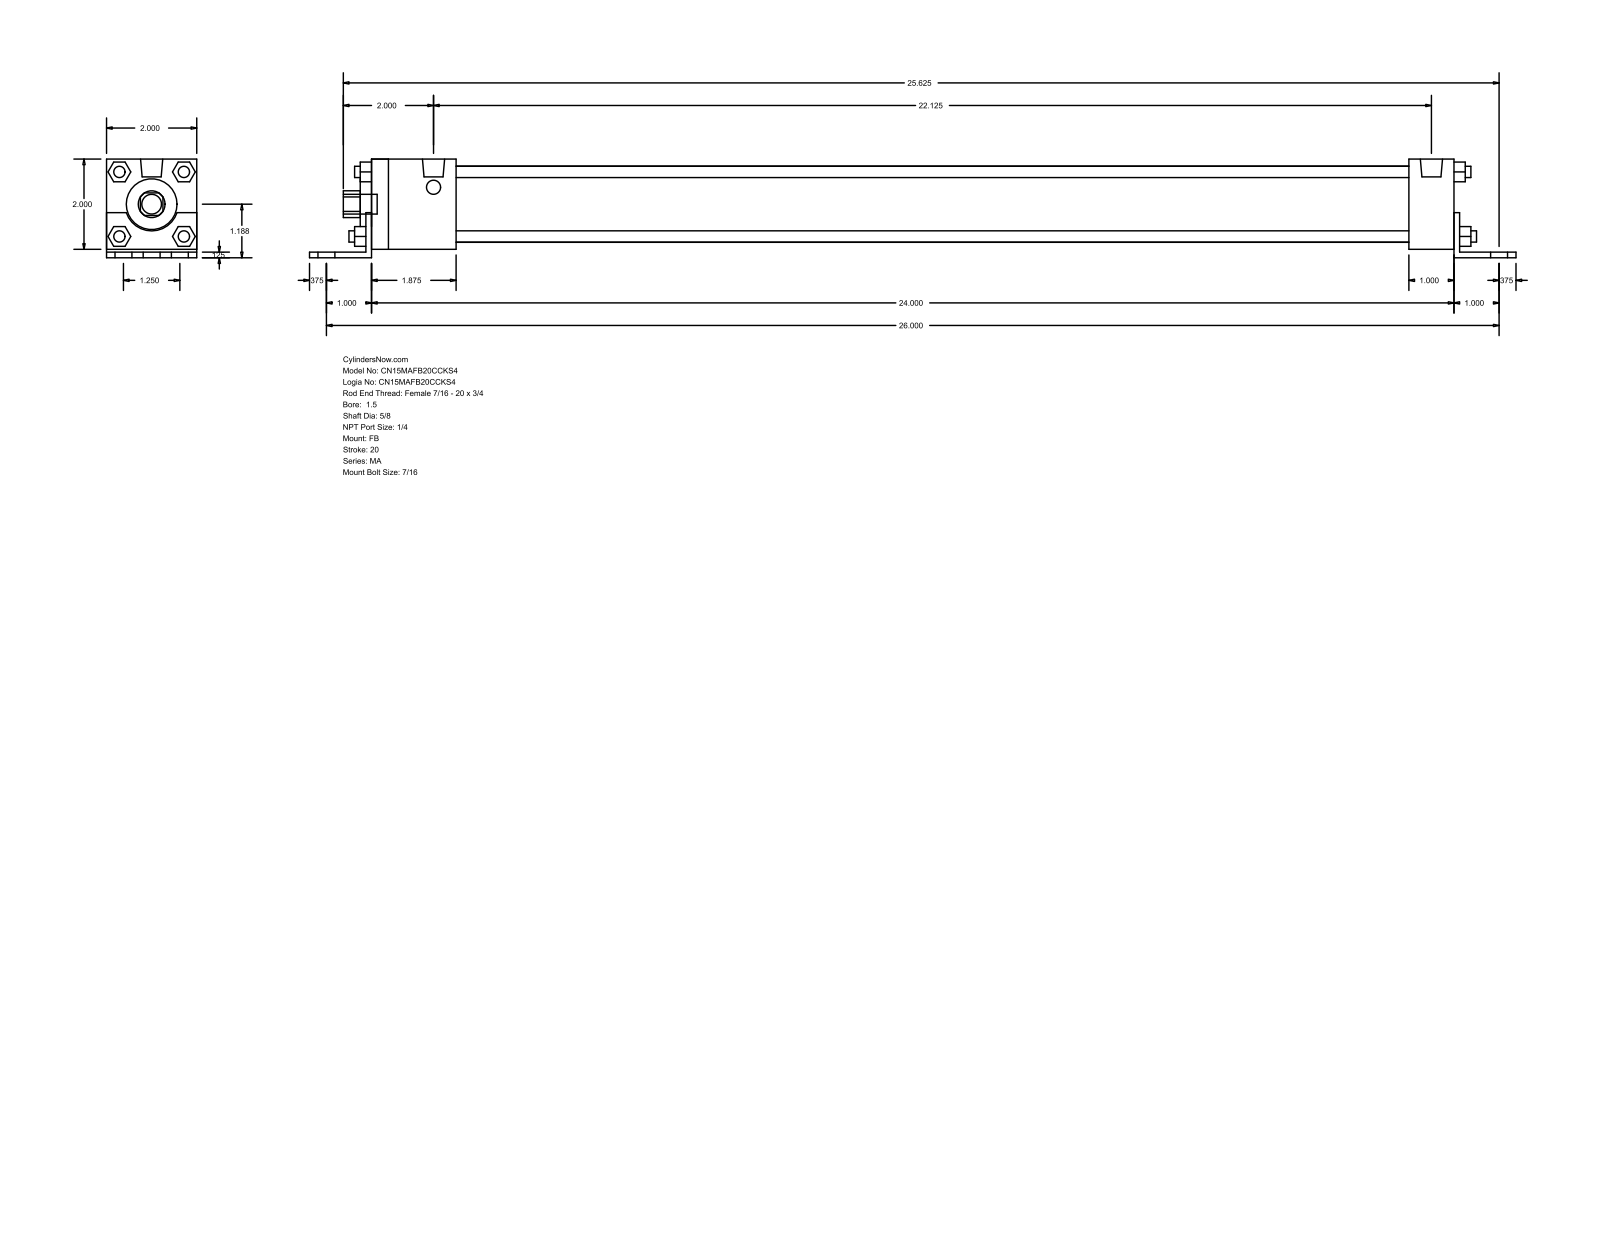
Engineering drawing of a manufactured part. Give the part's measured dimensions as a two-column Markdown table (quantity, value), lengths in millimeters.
| quantity | value |
| --- | --- |
| part name | MA_FB__0150_0.625 |
| STEP written by | GSSL Pune (CONFIG_CONTROL_DESIGN) |
| units | millimeters |
| bodies | 0 solids, 140 faces (105 planar, 35 cylindrical, 0 other) |
| overall size | 679.45 × 55.56 × 50.8 |
| round holes (diameter × count) | 15.88 × 1, 28.57 × 1, 42.93 × 1 |
| round bosses / shafts (diameter × count) | 11.11 × 7, 7.94 × 4, 6.35 × 4, 12.49 × 2 |
| partial cylindrical surfaces (radius × count) | 7.54 × 1, 15.05 × 1 |
| main face-to-face distances | 50.8, 3.17, 4.76, 55.56, 1.59, 52.39, 25.4, 615.95, 6.35, 609.6 |
